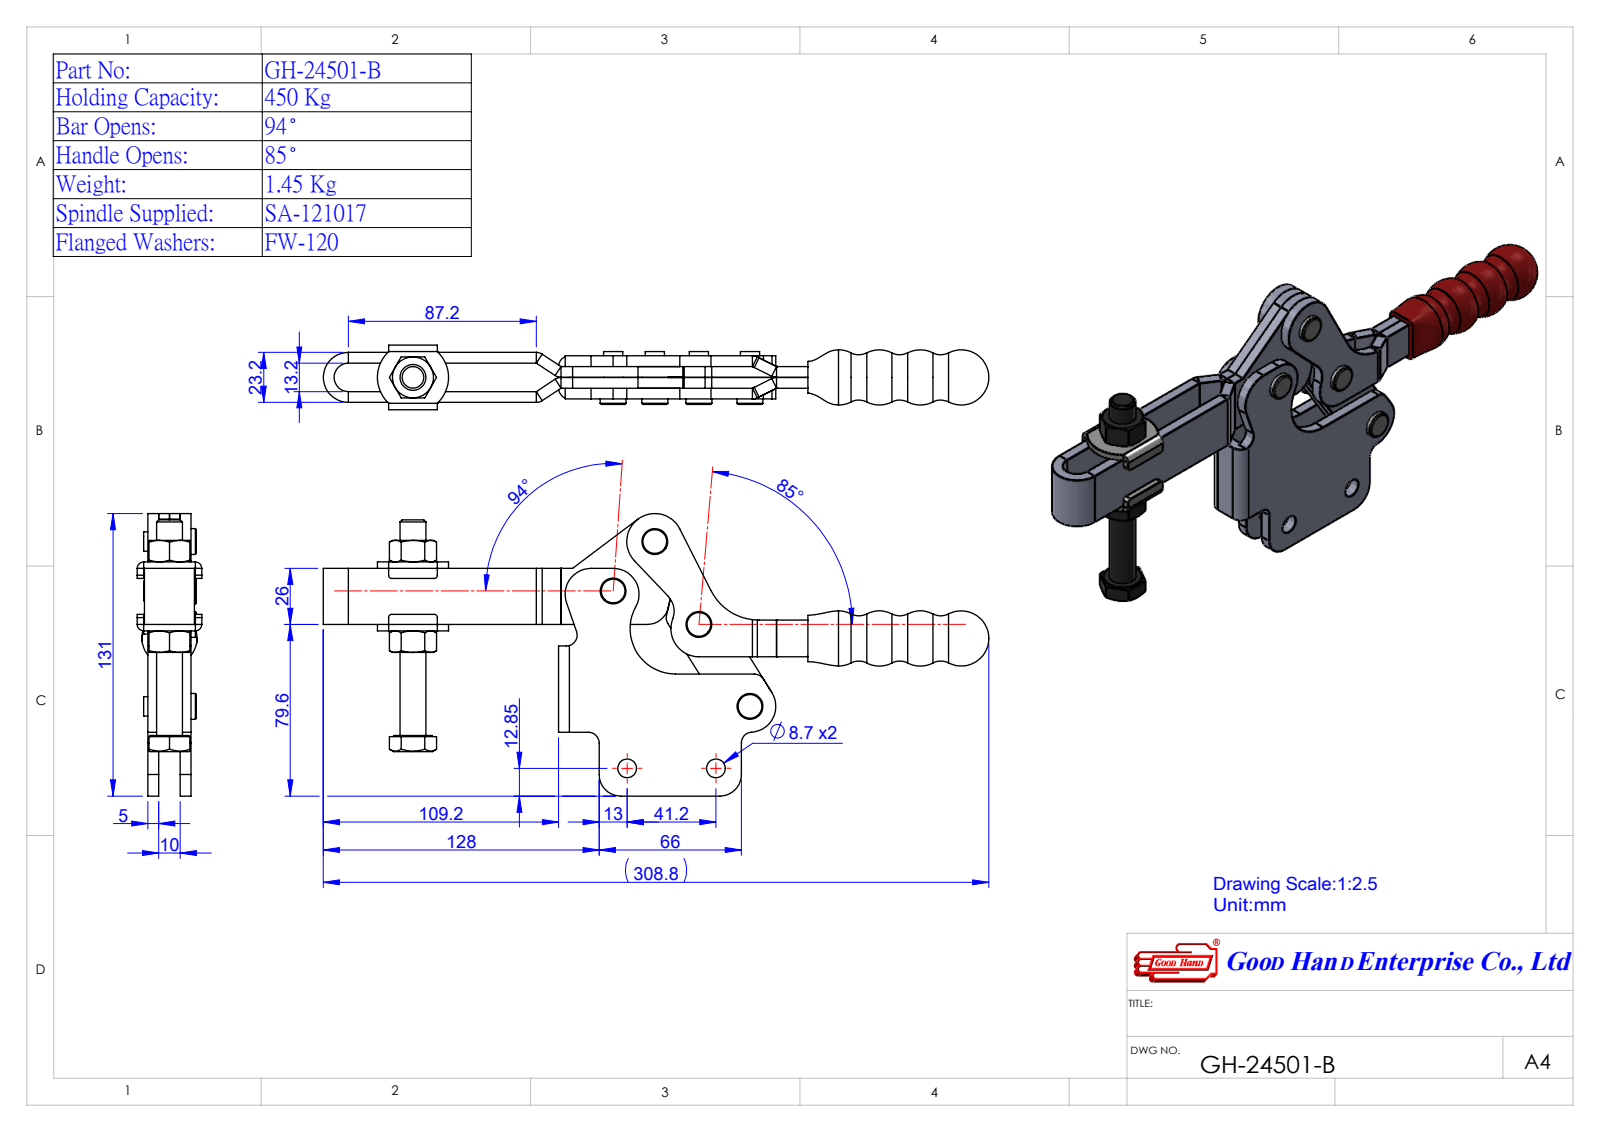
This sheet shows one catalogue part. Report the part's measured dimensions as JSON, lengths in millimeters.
{"part_name": "Group5^GH-24501-B(簡化)-1; Group4^GH-24501-B(簡化); GH-24501-B(簡化)-1; 124502B08-1^GH-24501-B(簡化)-1 (+2 more)", "step_written_by": "SolidWorks 2016 (AUTOMOTIVE_DESIGN)", "units": "millimeters", "bodies": {"solids": 4, "faces": 350, "planar": 130, "cylindrical": 141, "other": 79}, "overall_size": [308.7, 131.04, 31.4], "volume_mm3": 201448, "surface_area_mm2": 90754, "round_holes": [[8, 4], [8.7, 2], [10.2, 1], [12, 1], [13, 1]], "round_bosses_or_shafts": [[12, 4], [8.95, 4]], "partial_cylinders_radius": [[5, 7], [10, 5], [1, 4], [4.2, 4], [12, 3], [4.85, 2], [7.9, 2], [13, 2]], "face_to_face_distances": [5, 10, 15, 16.6, 1.6, 6.6, 11.6, 20, 21.6, 18.2], "hole_center_spacings": [30, 32.81, 41.2, 42.7, 43.55, 44.79, 63.84, 67.22]}
